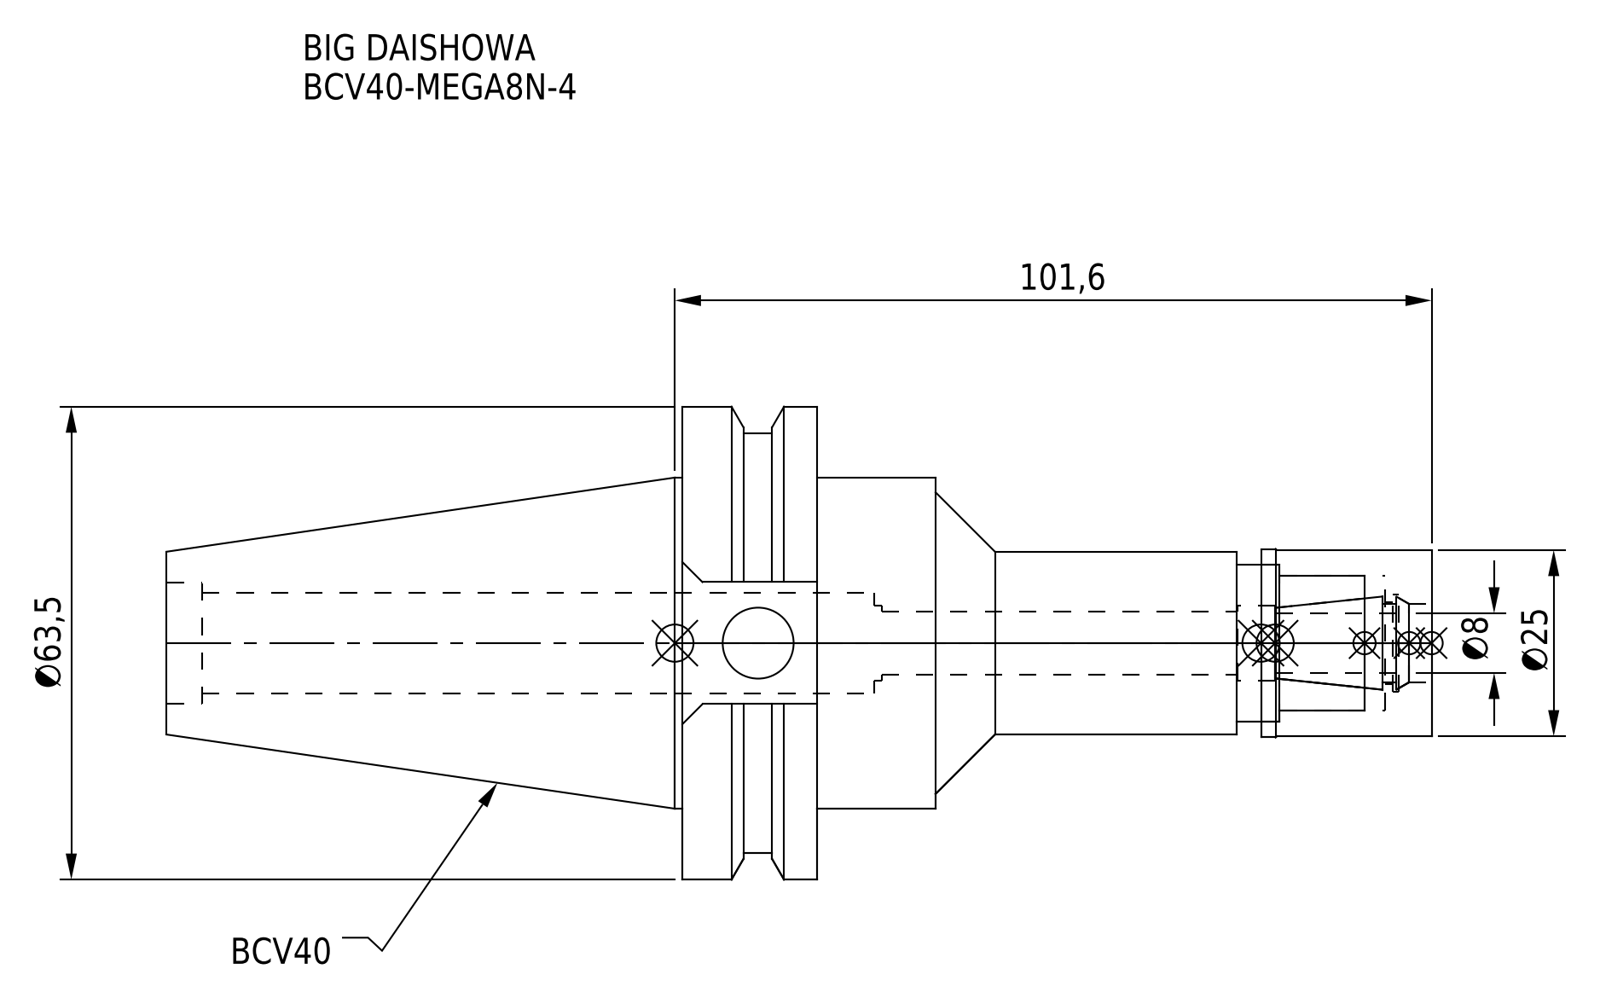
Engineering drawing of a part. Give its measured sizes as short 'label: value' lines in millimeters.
name: BCV40MN08040-080_ASM.stp; BCV40-MEGA8N-4-080.stp; BCV40-MEGA8N-4_1.stp; BCV40-MEGA8N-4-080-FreeParts (+3 more)
written by: SolidWorks 2019 (CONFIG_CONTROL_DESIGN)
unit: mm
bodies: 2 solids, 91 faces (33 planar, 44 cylindrical, 14 other)
size: 169.85 × 63.5 × 61.35
volume: 156 371 mm³; area: 32 746 mm²
holes: 1× ⌀8.4, 1× ⌀9.53, 1× ⌀10, 1× ⌀10.5, 1× ⌀11, 1× ⌀13, 1× ⌀13.6, 1× ⌀16.32, 1× ⌀18, 1× ⌀21
bosses: 1× ⌀63.5, 1× ⌀56.36, 1× ⌀44.45, 1× ⌀25.3, 1× ⌀25, 1× ⌀24.5
face distances: 18.05, 82.55, 100.6, 169.85, 87.3, 69.25, 66.6, 15.95, 34, 103.25
